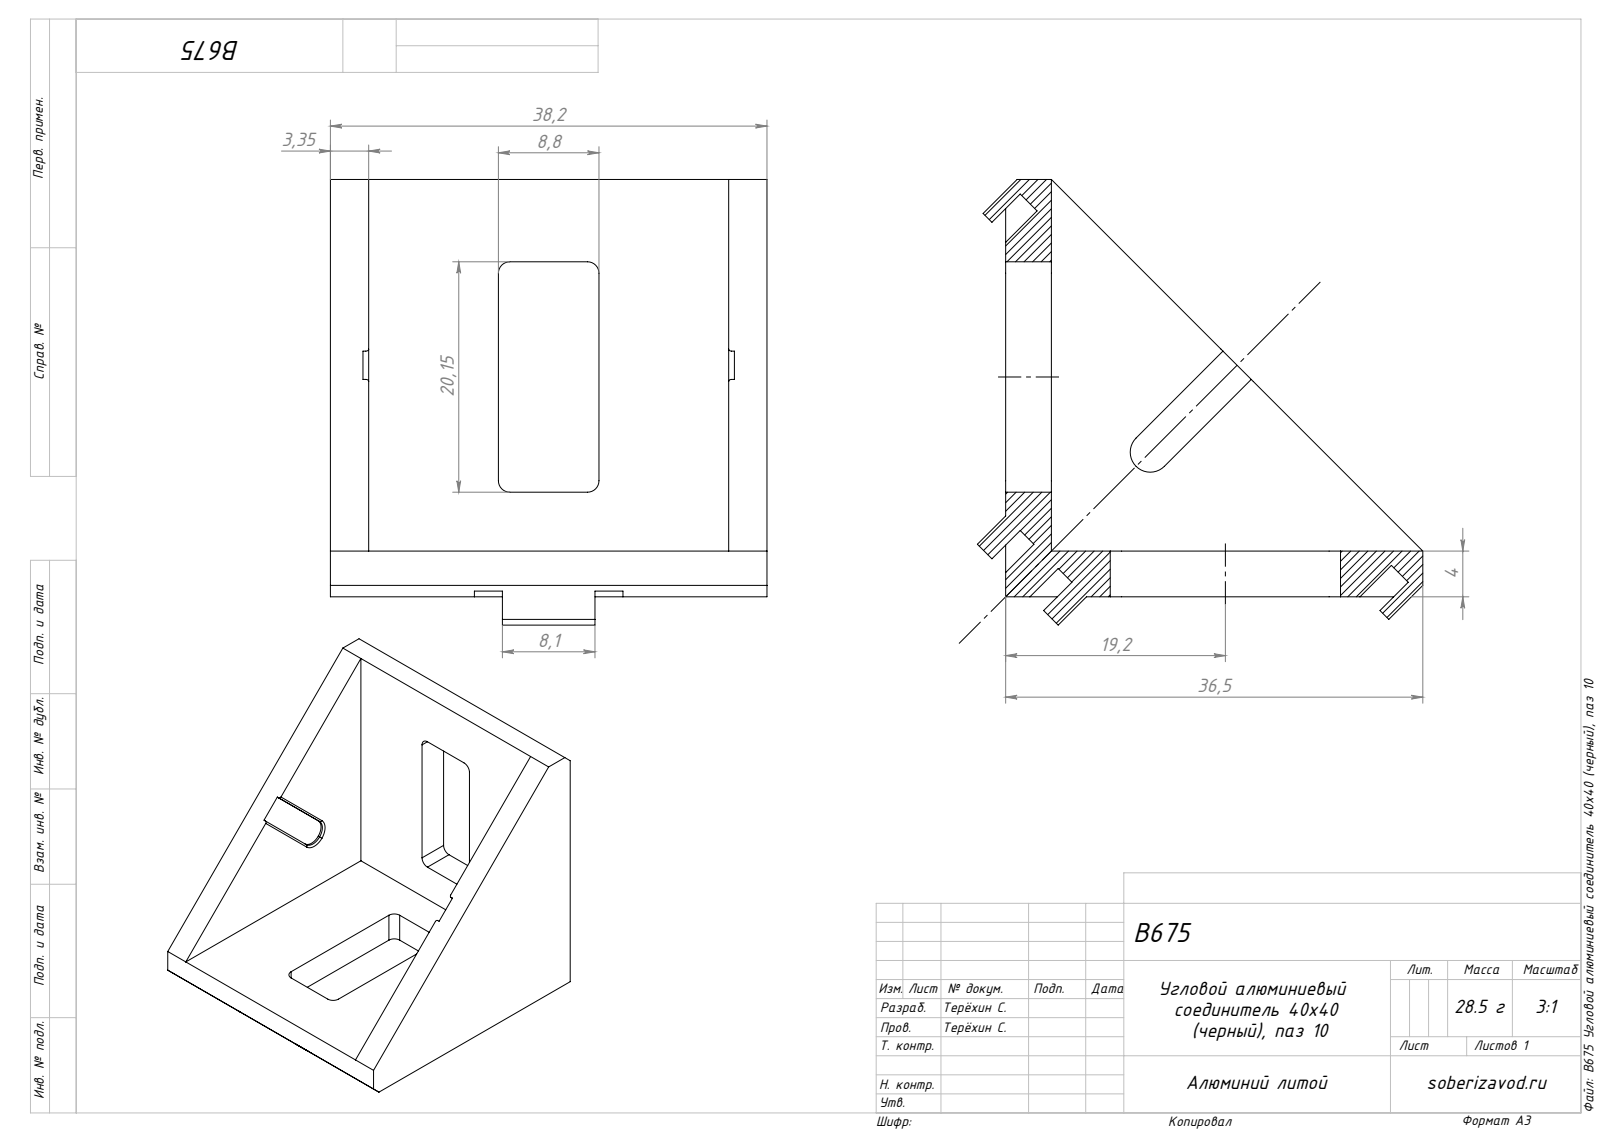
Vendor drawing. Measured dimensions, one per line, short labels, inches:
name: B675 Угловой алюминиевый соединитель 40х40 (черный), паз 10_00; Сборка2
written by: SolidWorks 2025 (AUTOMOTIVE_DESIGN)
unit: in
bodies: 1 solid, 161 faces (108 planar, 48 cylindrical, 5 other)
size: 1.535 × 1.535 × 1.504
volume: 0.645 in³; area: 13.78 in²
rounds: 40× R0.039, 4× R0.01, 1× R0.069
face distances: 0.157, 0.132, 1.372, 1.504, 1.24, 0.13, 0.028, 0.793, 0.447, 0.579
